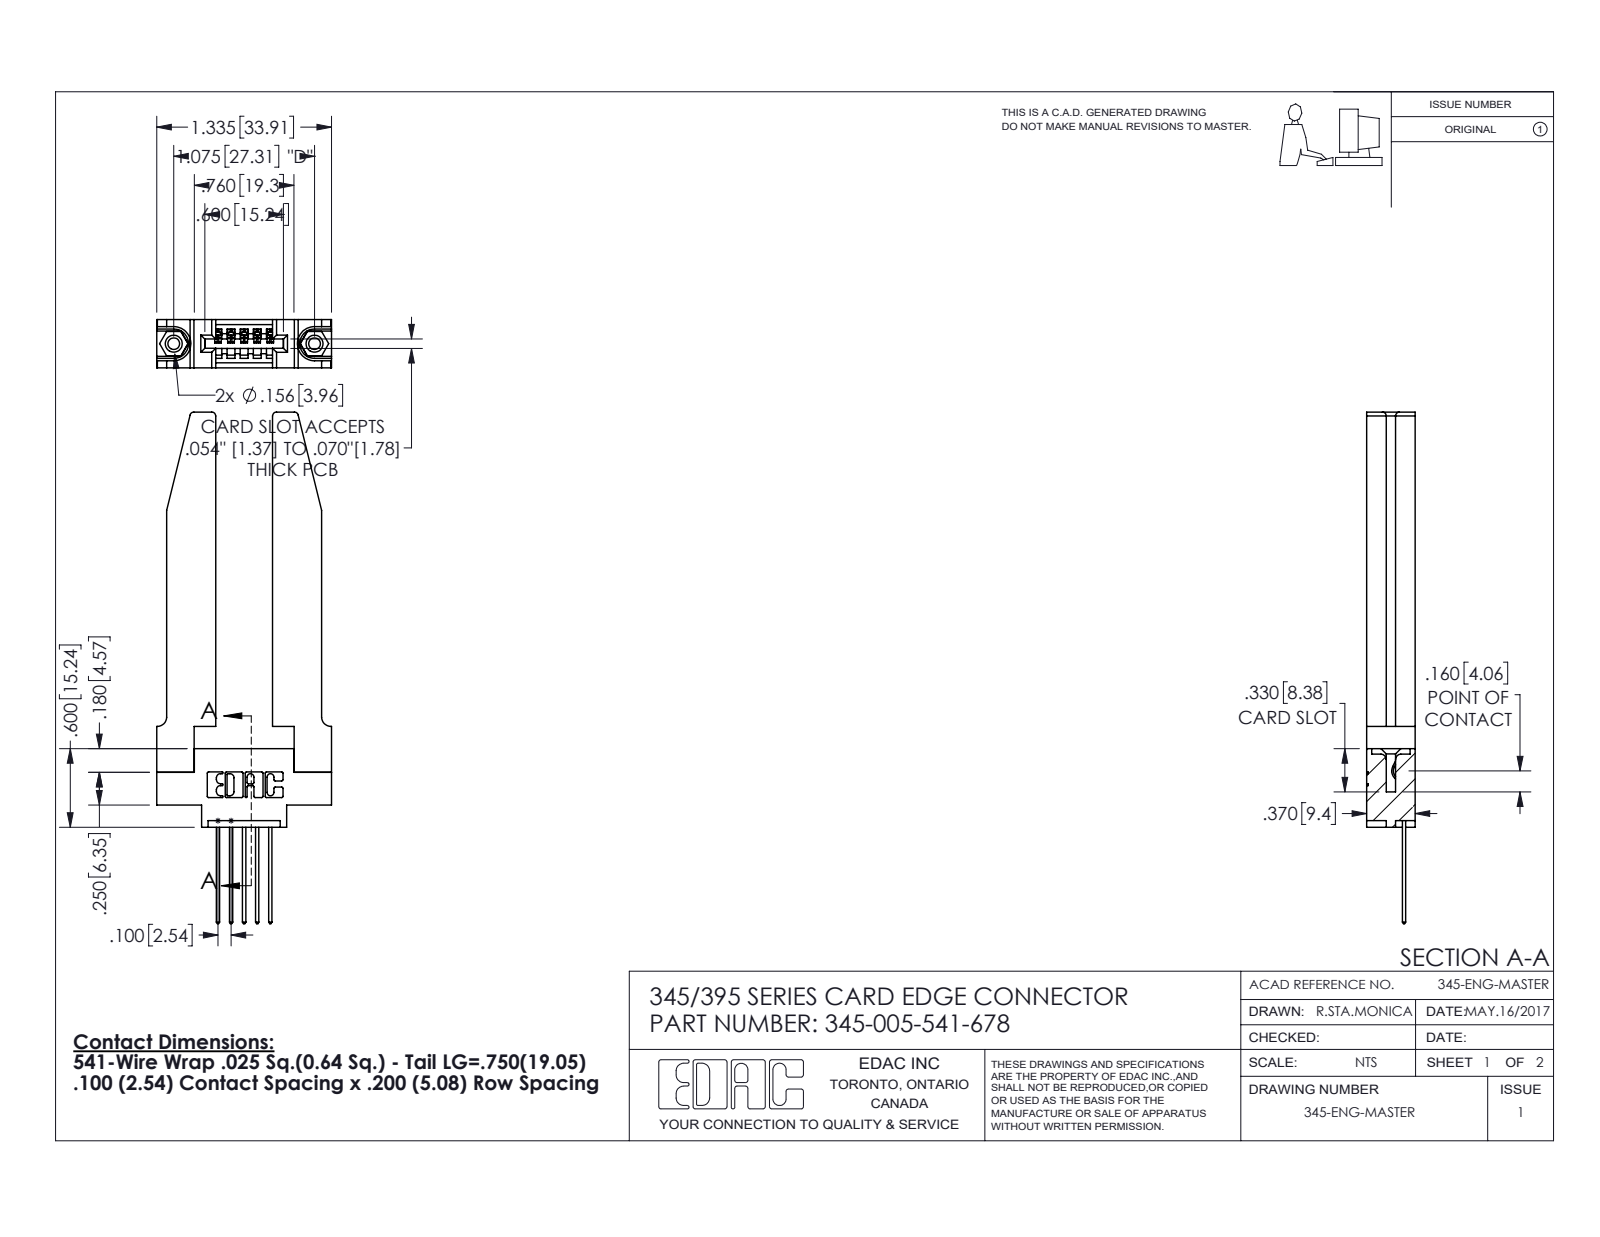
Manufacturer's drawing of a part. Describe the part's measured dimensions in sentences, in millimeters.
The part is named "345-220-078_345-220-078; 345-005-541-678; 345-250-001_345-250-001-102; 345 Part_0.170 Offset - 0.156 Dia-TH (+1 more)". Its 3-D file was written by "SolidWorks 2016 (CONFIG_CONTROL_DESIGN)". It is 10 solids with 654 faces: 426 planar, 176 cylindrical and 52 other. Overall it measures 99.2 by 33.9 by 9.4 millimeters. Its volume is 10 600 cubic millimeters and its surface area 10 320 square millimeters. Round holes: 2 of diameter 2.3, 2 of diameter 3.2, 2 of diameter 4, 1 of diameter 1.6. Round bosses or shafts: 2 of diameter 3.9. Partial cylindrical surfaces (rounded edges, fillets, slot ends): 22 of radius 0.3, 10 of radius 0.2, 10 of radius 0.3, 8 of radius 0.8, 6 of radius 0.2, 6 of radius 0.8, 3 of radius 0.7, 2 of radius 0.8. The main face-to-face distances are 9.4, 3.8, 5.6, 11, 3.8, 1.8, 7.6, 2, 2.4, 1.8. The hole center spacings are 6.9, 21.5, 27.3.
